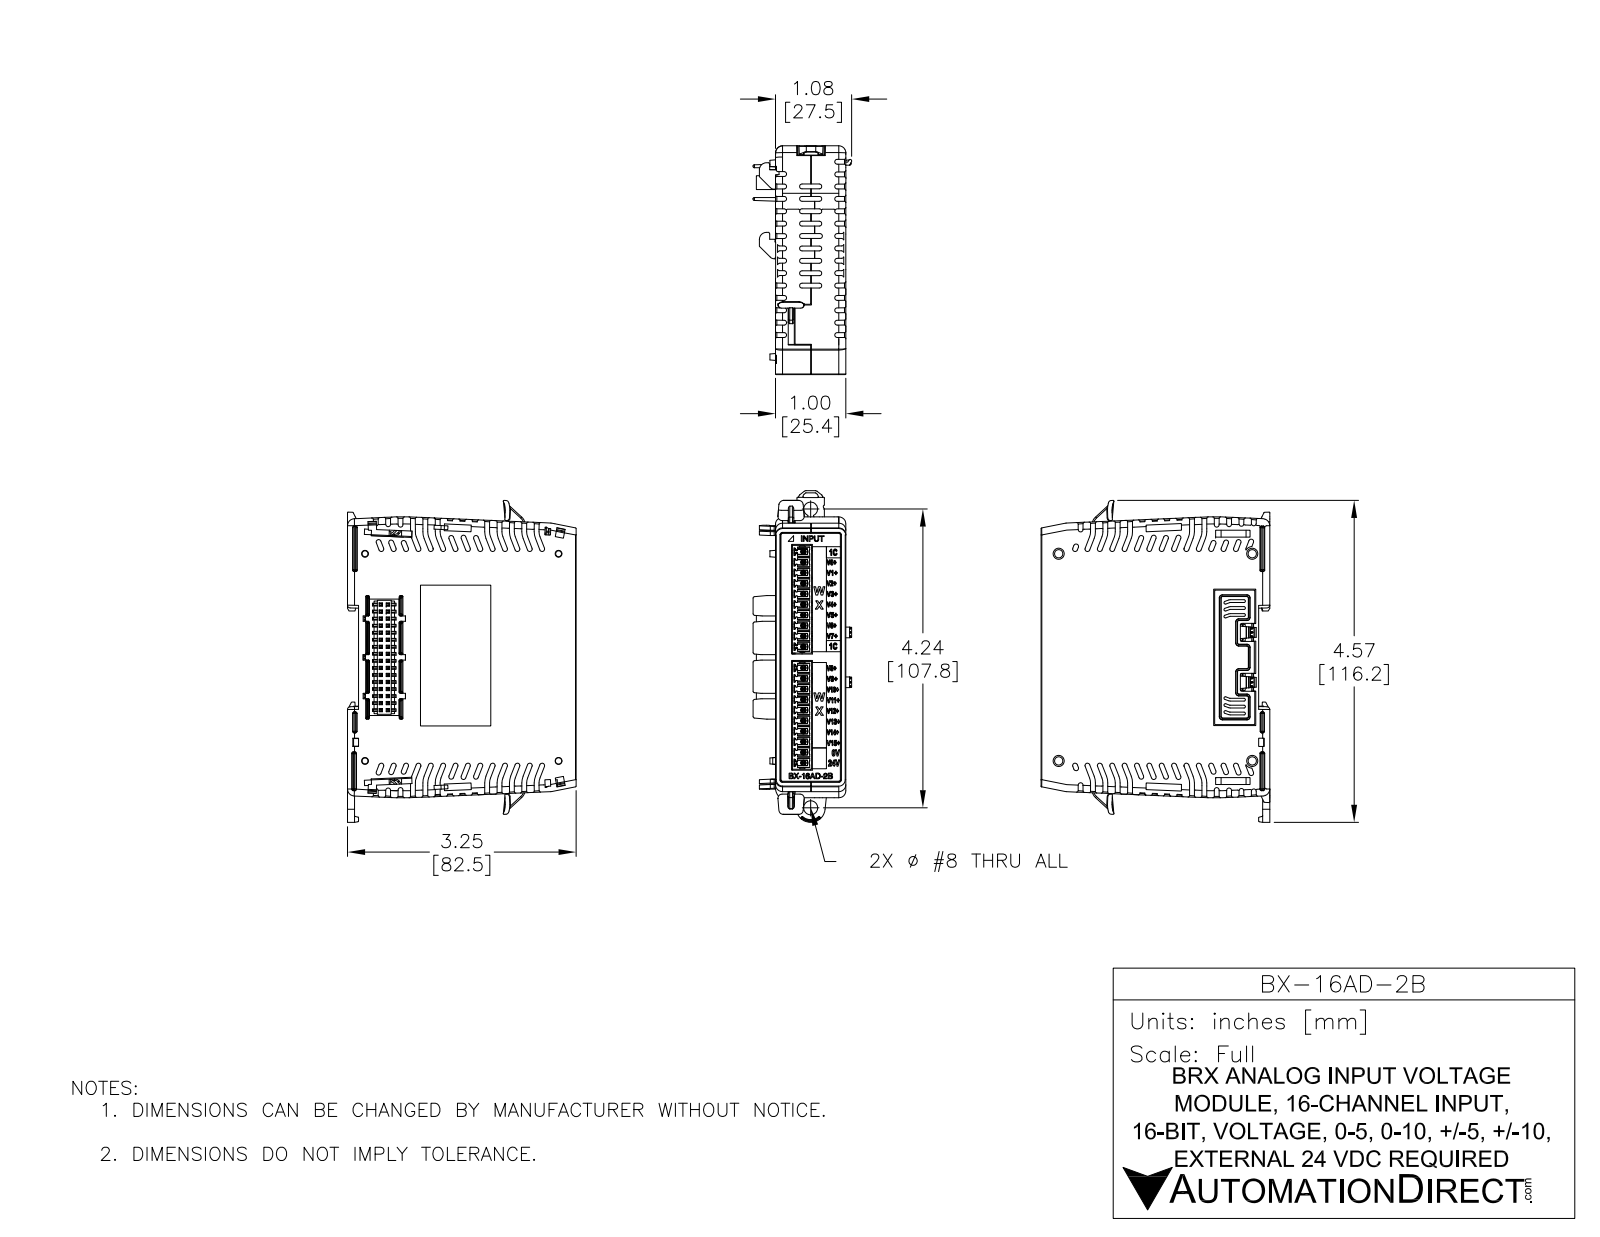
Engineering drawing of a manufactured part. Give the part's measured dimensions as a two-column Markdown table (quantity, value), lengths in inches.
| quantity | value |
| --- | --- |
| part name | BX-16AD-2B |
| STEP written by | SolidWorks 2017 (AUTOMOTIVE_DESIGN) |
| units | inches |
| bodies | 10 solids, 4976 faces (3563 planar, 627 cylindrical, 786 other) |
| overall size | 4.586 × 3.25 × 1.401 |
| volume | 9.457 in³ |
| surface area | 89.26 in² |
| round holes (diameter × count) | 0.016 × 8, 0.016 × 2, 0.118 × 2, 0.118 × 2, 0.199 × 1 |
| round bosses / shafts (diameter × count) | 0.111 × 2, 0.059 × 2, 0.071 × 1 |
| partial cylindrical surfaces (radius × count) | 0.02 × 109, 0.008 × 103, 0.005 × 48, 0.062 × 20, 0.012 × 16, 0.014 × 16, 0.01 × 14, 0.008 × 12 |
| main face-to-face distances | 1, 0.835, 0.165, 3.053, 0.209, 0.627, 0.791, 3.063, 2.053, 1.01 |
| hole center spacings | 0.15, 0.3, 0.45, 0.6, 0.75, 1.651, 0.9, 1.501 |
